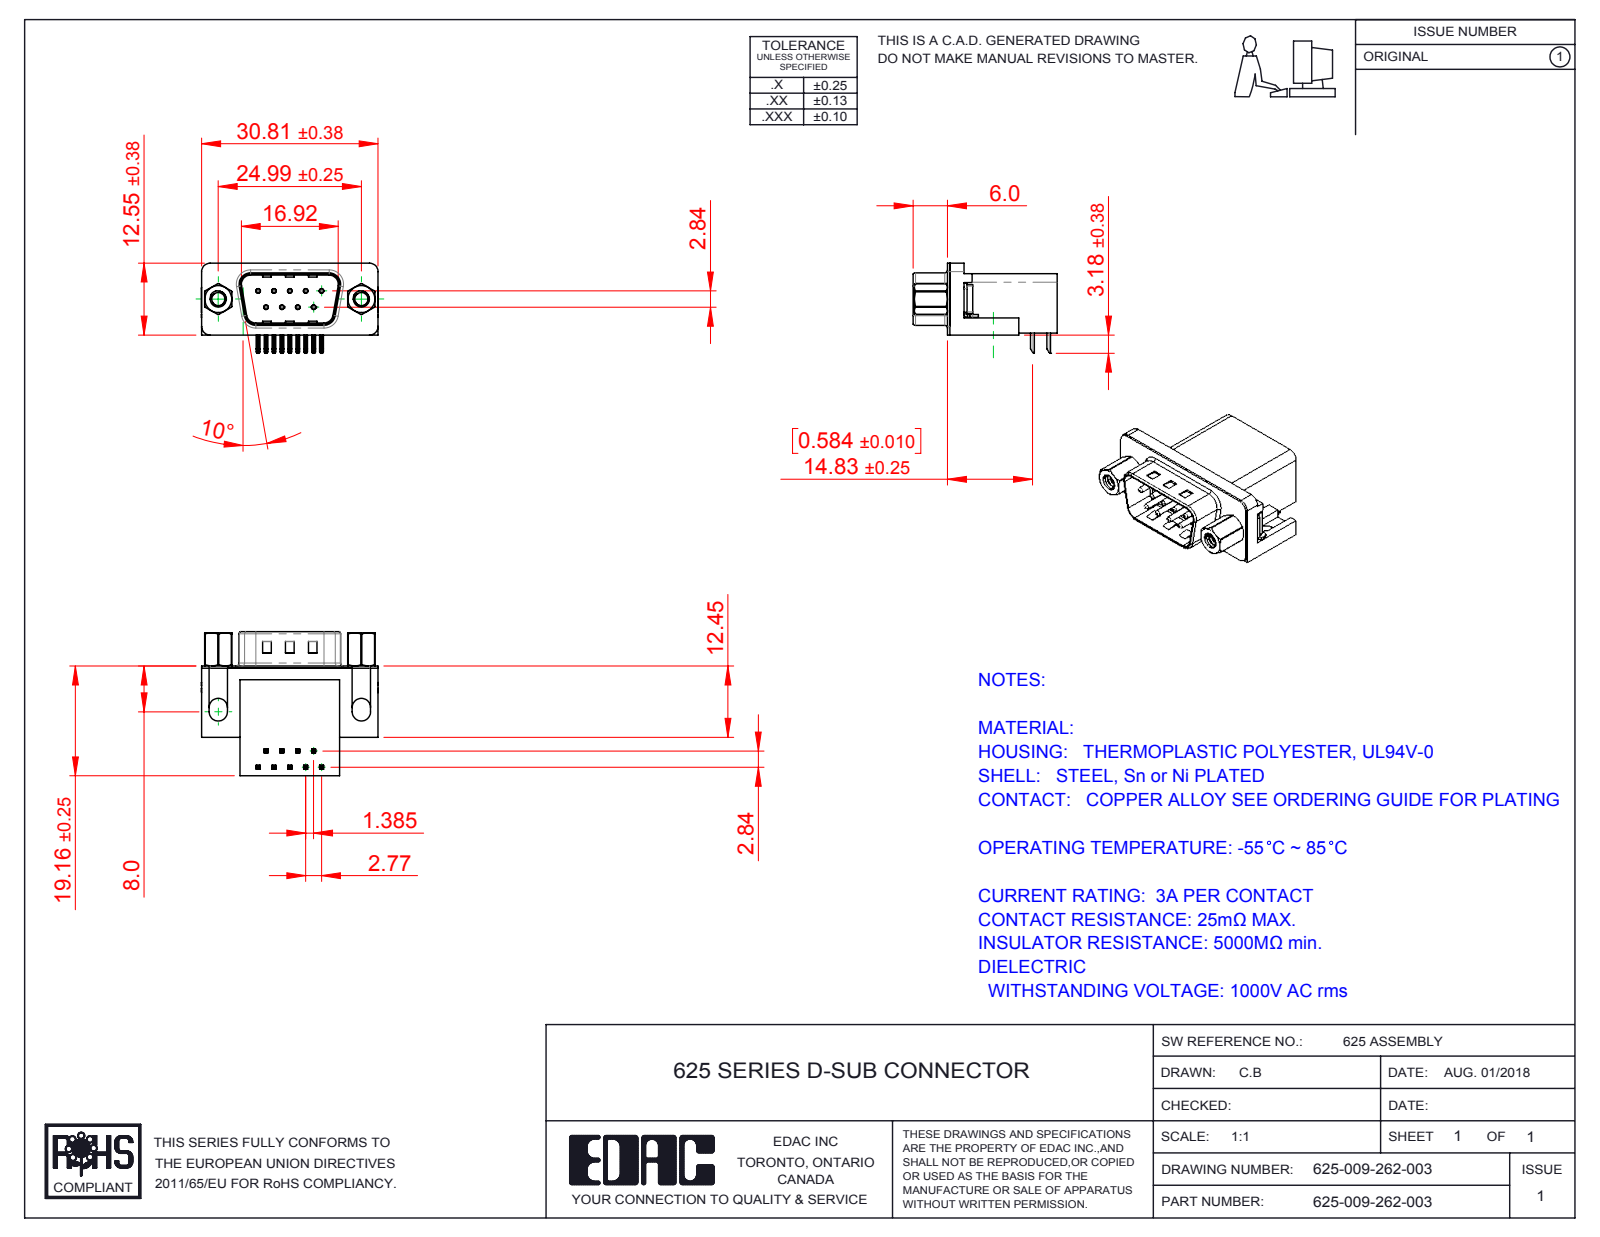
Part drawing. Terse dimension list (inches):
name: 625 Contact Top; 625 Contact Bottom; 625 Shell_9 Socket; 625 Housing_9 Socket (+4 more)
written by: SolidWorks 2016 (CONFIG_CONTROL_DESIGN)
unit: in
bodies: 17 solids, 1117 faces (597 planar, 385 cylindrical, 135 other)
size: 1.216 × 0.991 × 0.619
volume: 0.284 in³; area: 8.215 in²
holes: 9× ⌀0.014, 9× ⌀0.031, 2× ⌀0.089, 2× ⌀0.09, 2× ⌀0.157, 2× ⌀0.189, 2× ⌀0.197
bosses: 9× ⌀0.03, 2× ⌀0.193, 2× ⌀0.187, 2× ⌀0.154, 2× ⌀0.11
rounds: 44× R0.01, 18× R0.005, 16× R0.039, 9× R0.02, 8× R0.059, 8× R0.063, 4× R0.035, 4× R0.079
face distances: 0.016, 0.407, 0.739, 0.754, 0.64, 0.098, 0.114, 0.014, 0.421, 0.264
hole spacings: 0.124, 0.109, 0.218, 0.198, 0.198, 0.327, 0.294, 0.295
